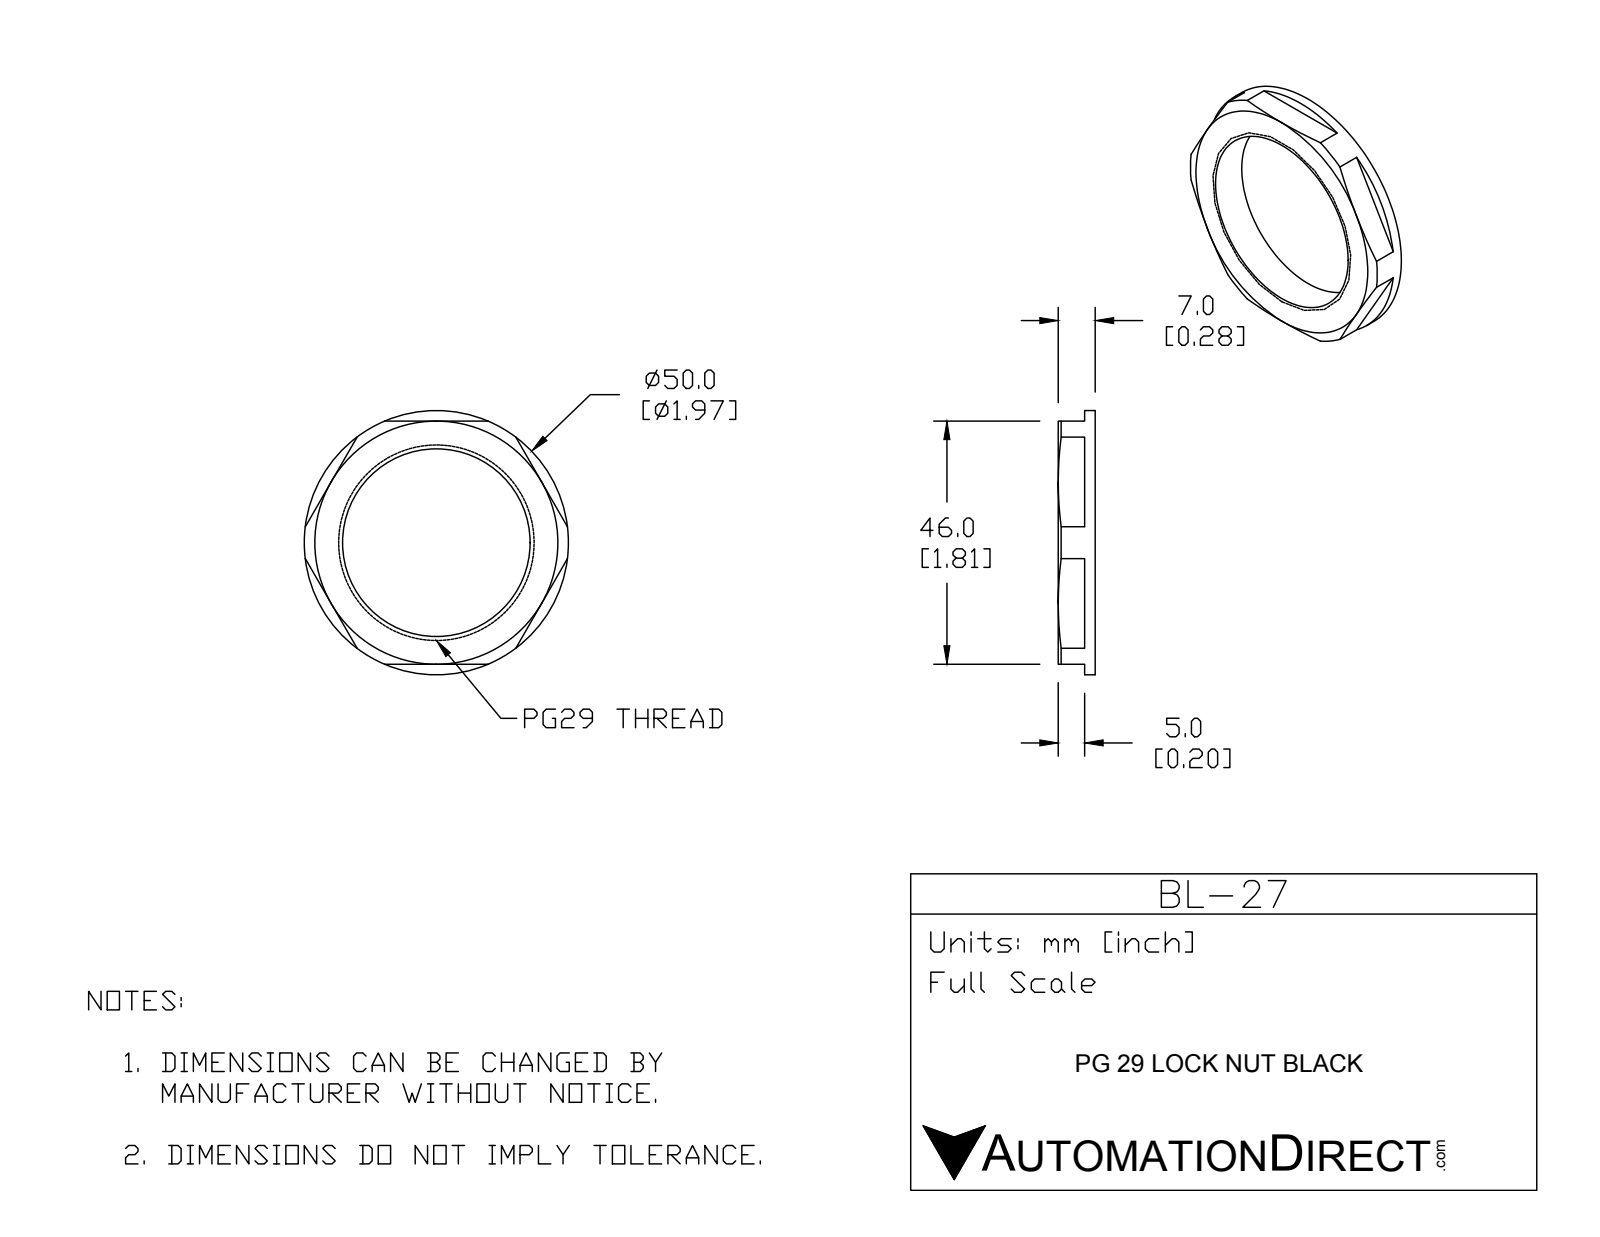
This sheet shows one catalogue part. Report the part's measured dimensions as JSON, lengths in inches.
{"part_name": "BL-27", "step_written_by": "SolidWorks 2015 (CONFIG_CONTROL_DESIGN)", "units": "inches", "bodies": {"solids": 1, "faces": 33, "planar": 17, "cylindrical": 10, "other": 6}, "overall_size": [1.969, 1.969, 0.276], "volume_in3": 0.366, "surface_area_in2": 5.859, "round_holes": [[0.059, 3], [1.398, 1]], "round_bosses_or_shafts": [[1.969, 1]], "face_to_face_distances": [0.276, 1.811, 0.079, 0.197, 0.067, 0.264], "hole_center_spacings": [0.927, 1.606, 0.927, 1.606]}
